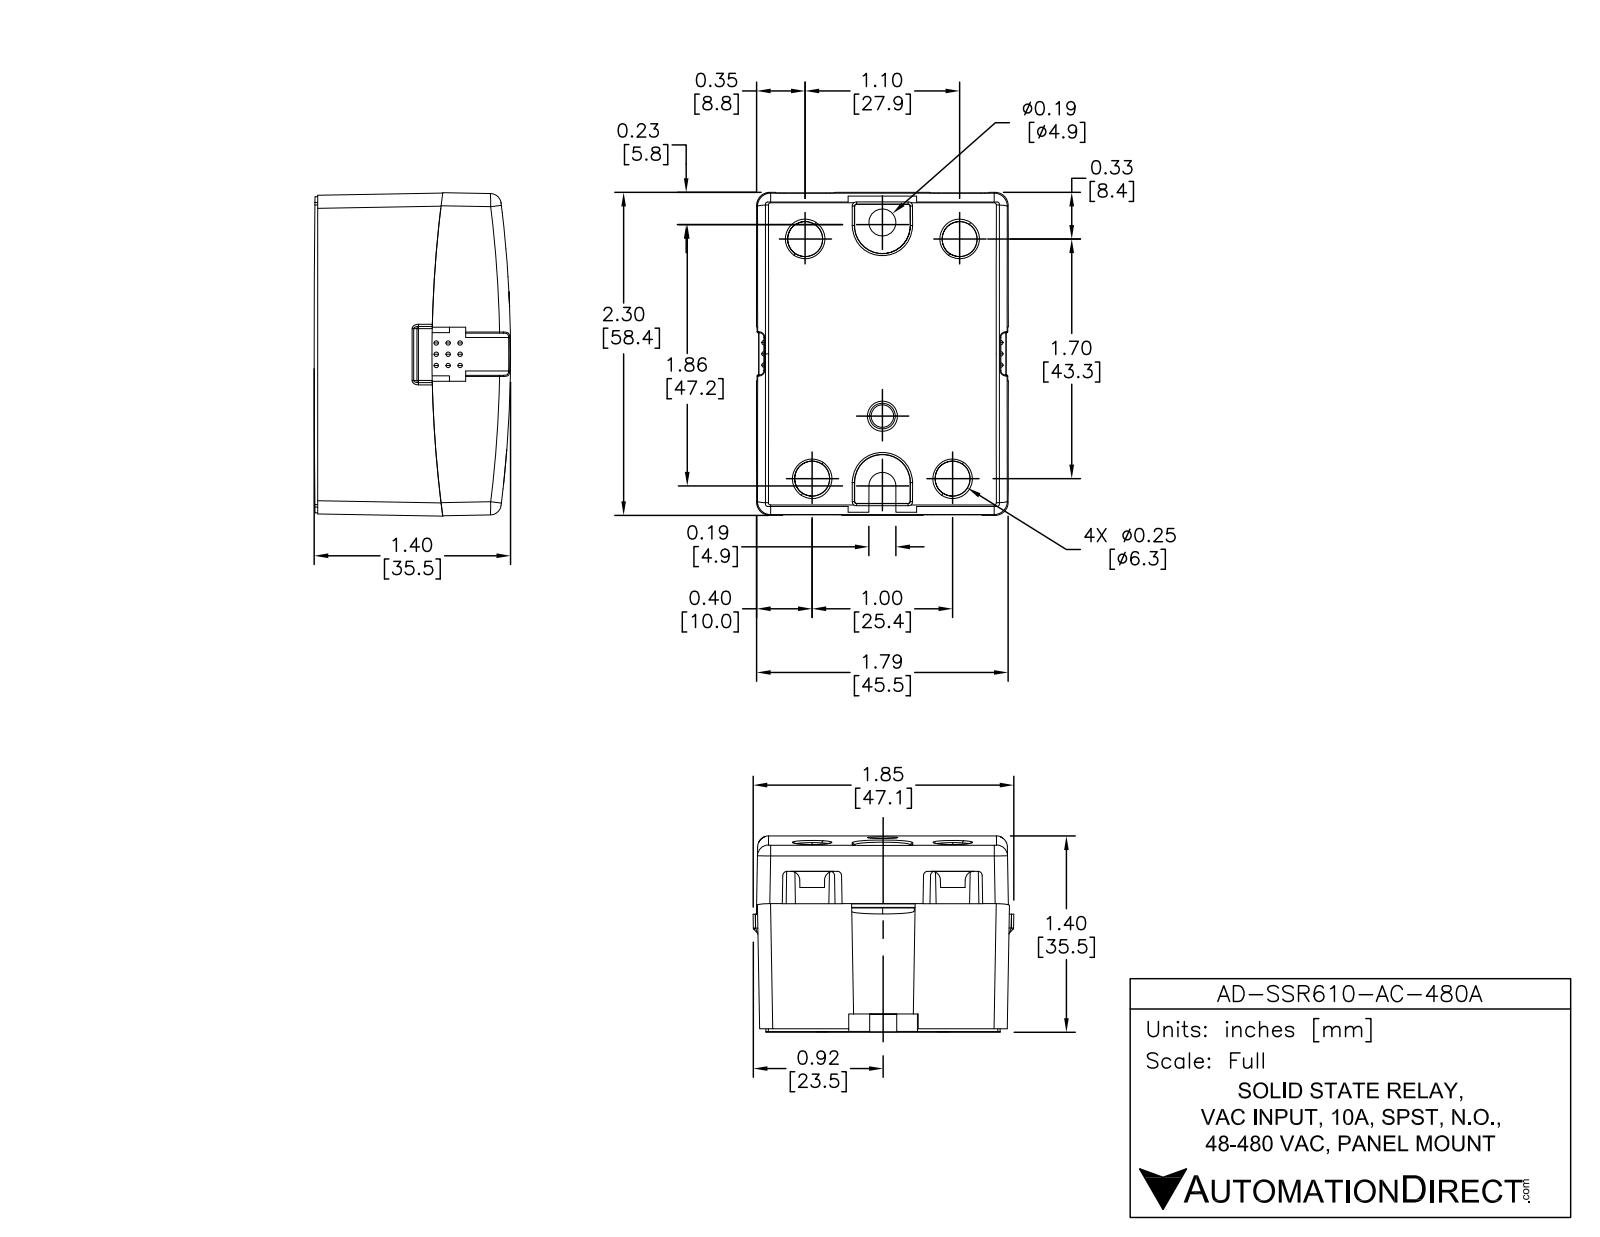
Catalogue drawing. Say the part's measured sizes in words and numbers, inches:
The part is named "AD-SSR610-AC-480A". Its 3-D file was written by "SolidWorks 2013 (AUTOMOTIVE_DESIGN)". It is 3 solids with 251 faces: 145 planar, 95 cylindrical and 11 other. Overall it measures 2.3 by 1.79 by 1.4 inches. Its volume is 5.14 cubic inches and its surface area 26.41 square inches. Round holes: 4 of diameter 0.25, 1 of diameter 0.19. Round bosses or shafts: 2 of diameter 0.4, 2 of diameter 0.35, 2 of diameter 0.3, 2 of diameter 0.25, 2 of diameter 0.2, 2 of diameter 0.2. Partial cylindrical surfaces (rounded edges, fillets, slot ends): 6 of radius 0.03, 4 of radius 0.01, 4 of radius 0.04, 4 of radius 0.5, 2 of radius 0.194, 1 of radius 0.095, 1 of radius 0.5, 1 of radius 0.5. The main face-to-face distances are 1.79, 2.3, 1.166, 0.25, 0.916, 0.671, 1.059, 0.5, 1.8, 0.08. The hole center spacings are 0.556, 0.565, 1, 1.1, 1.7, 1.701, 1.876, 1.879.
